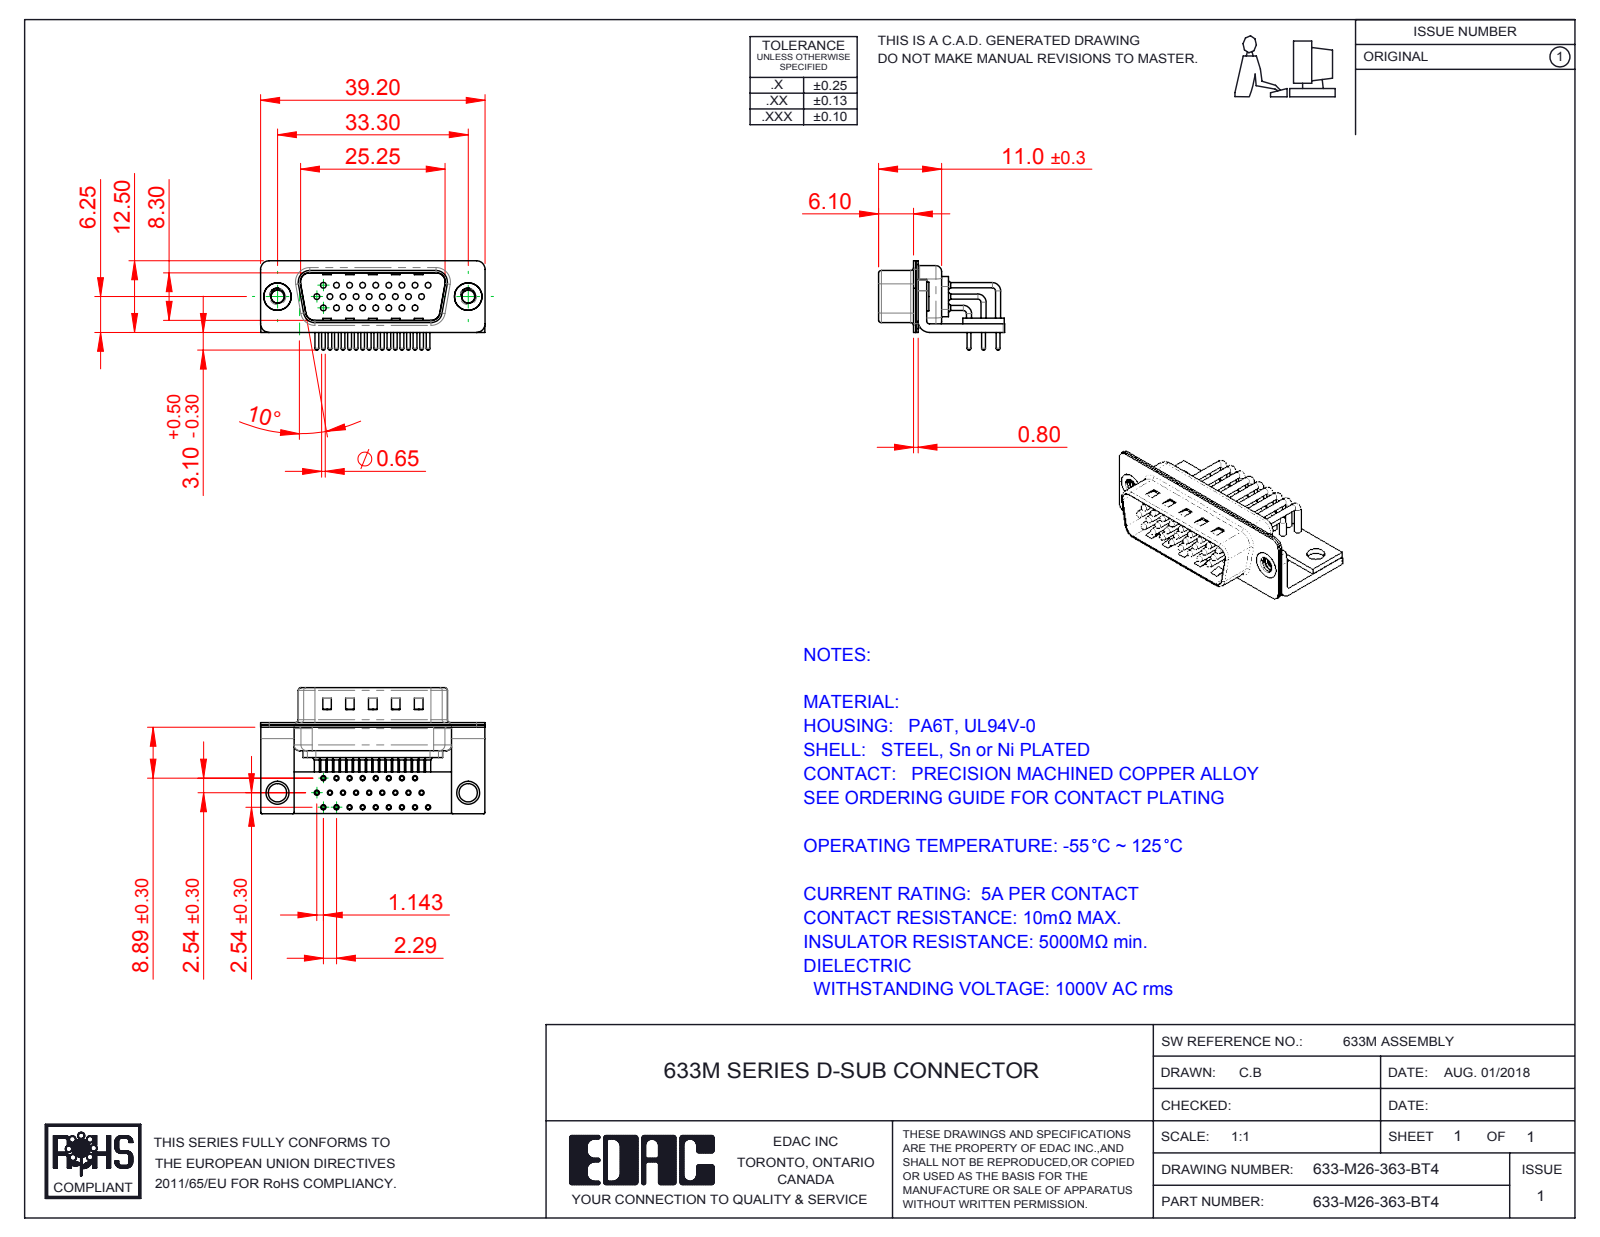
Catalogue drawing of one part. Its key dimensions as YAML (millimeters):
part_name: "633M Contact Row 2; 633M Housing_26 Contacts; 633-M26-363-BT4; 633M Stabilizer Board_26 Contacts (+6 more)"
step_written_by: "SolidWorks 2016 (CONFIG_CONTROL_DESIGN)"
units: millimeters
bodies: {solids: 34, faces: 3302, planar: 1829, cylindrical: 1143, other: 330}
overall_size: [39.2, 22, 15.6]
volume: 2620
surface_area: 7989
round_holes:
  - {diameter: 0.9, count: 26}
  - {diameter: 1, count: 26}
  - {diameter: 1.7, count: 26}
  - {diameter: 2, count: 26}
  - {diameter: 2.26, count: 2}
  - {diameter: 3.2, count: 2}
  - {diameter: 4, count: 2}
  - {diameter: 4.8, count: 2}
round_bosses_or_shafts:
  - {diameter: 1.5, count: 26}
  - {diameter: 0.9, count: 26}
  - {diameter: 0.65, count: 26}
  - {diameter: 5, count: 2}
  - {diameter: 4.9, count: 2}
partial_cylinders:
  - {radius: 1.01, count: 26}
  - {radius: 0.25, count: 16}
  - {radius: 1.5, count: 16}
  - {radius: 2, count: 13}
  - {radius: 0.5, count: 9}
  - {radius: 1.6, count: 8}
  - {radius: 0.6, count: 4}
  - {radius: 0.65, count: 4}
face_to_face_distances: [0.4, 1.5, 0.85, 0.8, 1.25, 1, 1.9, 10.4, 9.55, 2.5]
hole_center_spacings: [4.57, 2.29, 2.28, 3.96, 6.86, 4.27, 6.05, 2.78]
